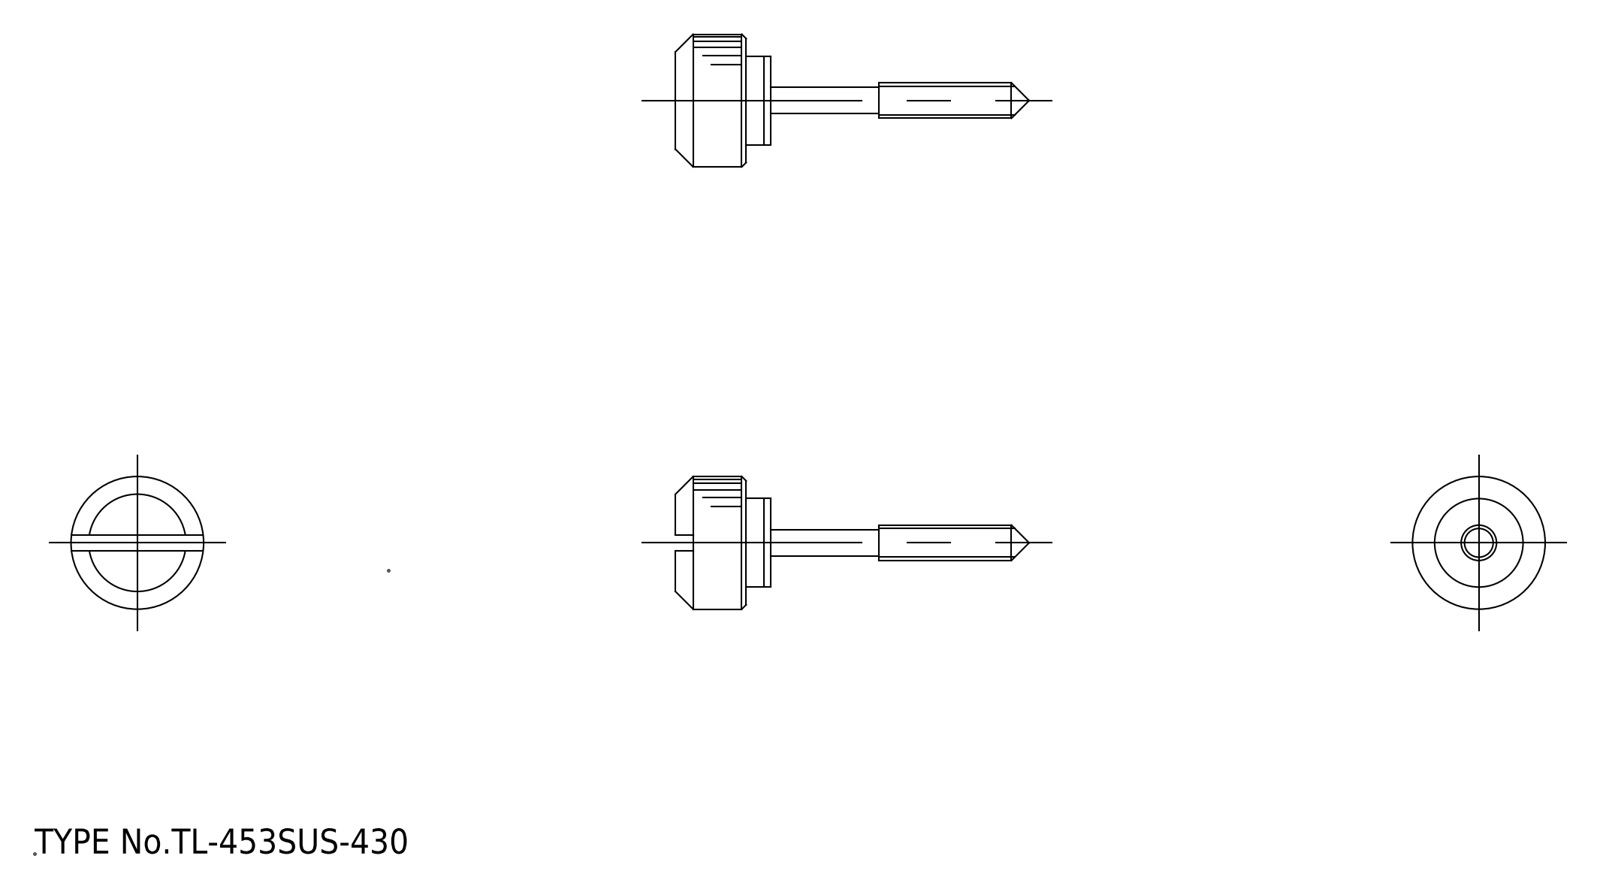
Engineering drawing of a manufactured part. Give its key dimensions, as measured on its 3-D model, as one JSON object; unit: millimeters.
{"part_name": "washer; knob", "step_written_by": "spGate 19.8.4 (****-****-****-****) (AUTOMOTIVE_DESIGN)", "units": "millimeters", "bodies": {"solids": 2, "faces": 38, "planar": 16, "cylindrical": 16, "other": 6}, "overall_size": [40, 15, 15], "volume_mm3": 1773, "surface_area_mm2": 1263, "round_bosses_or_shafts": [[15, 1], [10, 1], [4, 1], [3, 1]], "partial_cylinders_radius": [[0.8, 3], [1.55, 1]], "face_to_face_distances": [2, 8, 10, 10.8, 2.8, 0.8, 6, 8.8, 1.8, 23]}
